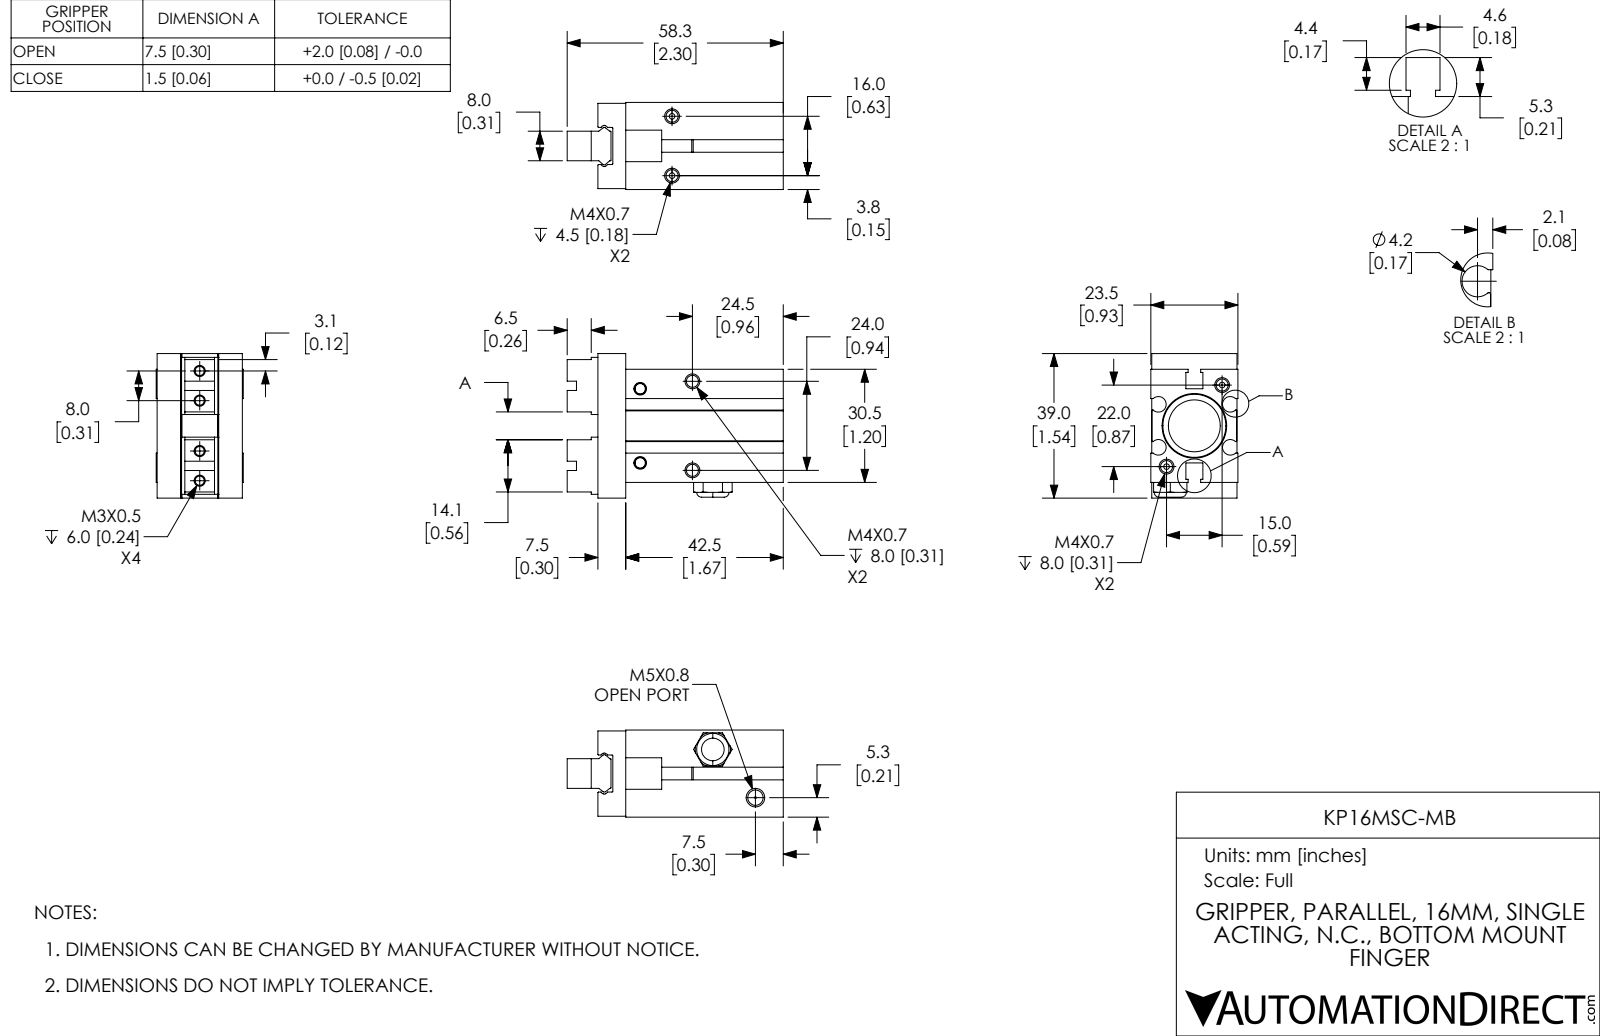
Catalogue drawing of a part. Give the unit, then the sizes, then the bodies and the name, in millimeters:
Units: millimetres
Overall size (bounding box): 58.3 × 39 × 23.5
Round holes (diameter × count): ⌀3.24 ×6, ⌀0.5 ×2, ⌀2.46 ×2, ⌀4.02 ×2, ⌀4.13 ×2, ⌀6.1 ×1, ⌀14 ×1, ⌀17 ×1
Partial cylindrical surfaces — rounded edges, fillets, slot ends (radius × count): R0.2 ×10, R2.1 ×4, R0.4 ×2, R0.5 ×2, R1 ×2, R1.23 ×2, R1.23 ×2
Main face-to-face distances: 7.5, 15.75, 4, 30.5, 23.25, 23.2, 13.75, 23.5, 3.5, 16
Hole centre spacings: 8.41, 13.31, 14.8, 26.87, 11.1, 16, 17.36, 18.2
Volume: 30 496 mm³ · Surface area: 13 456 mm²
Bodies: 3 solids, 263 faces (133 planar, 68 cylindrical, 62 other)
Part name (STEP PRODUCT): KP16MSC-MB; KP16MSC-MB-1; KP16MSC-MB-2; KP16MSC-MB-3
STEP written by: SolidWorks 2017 (CONFIG_CONTROL_DESIGN)
